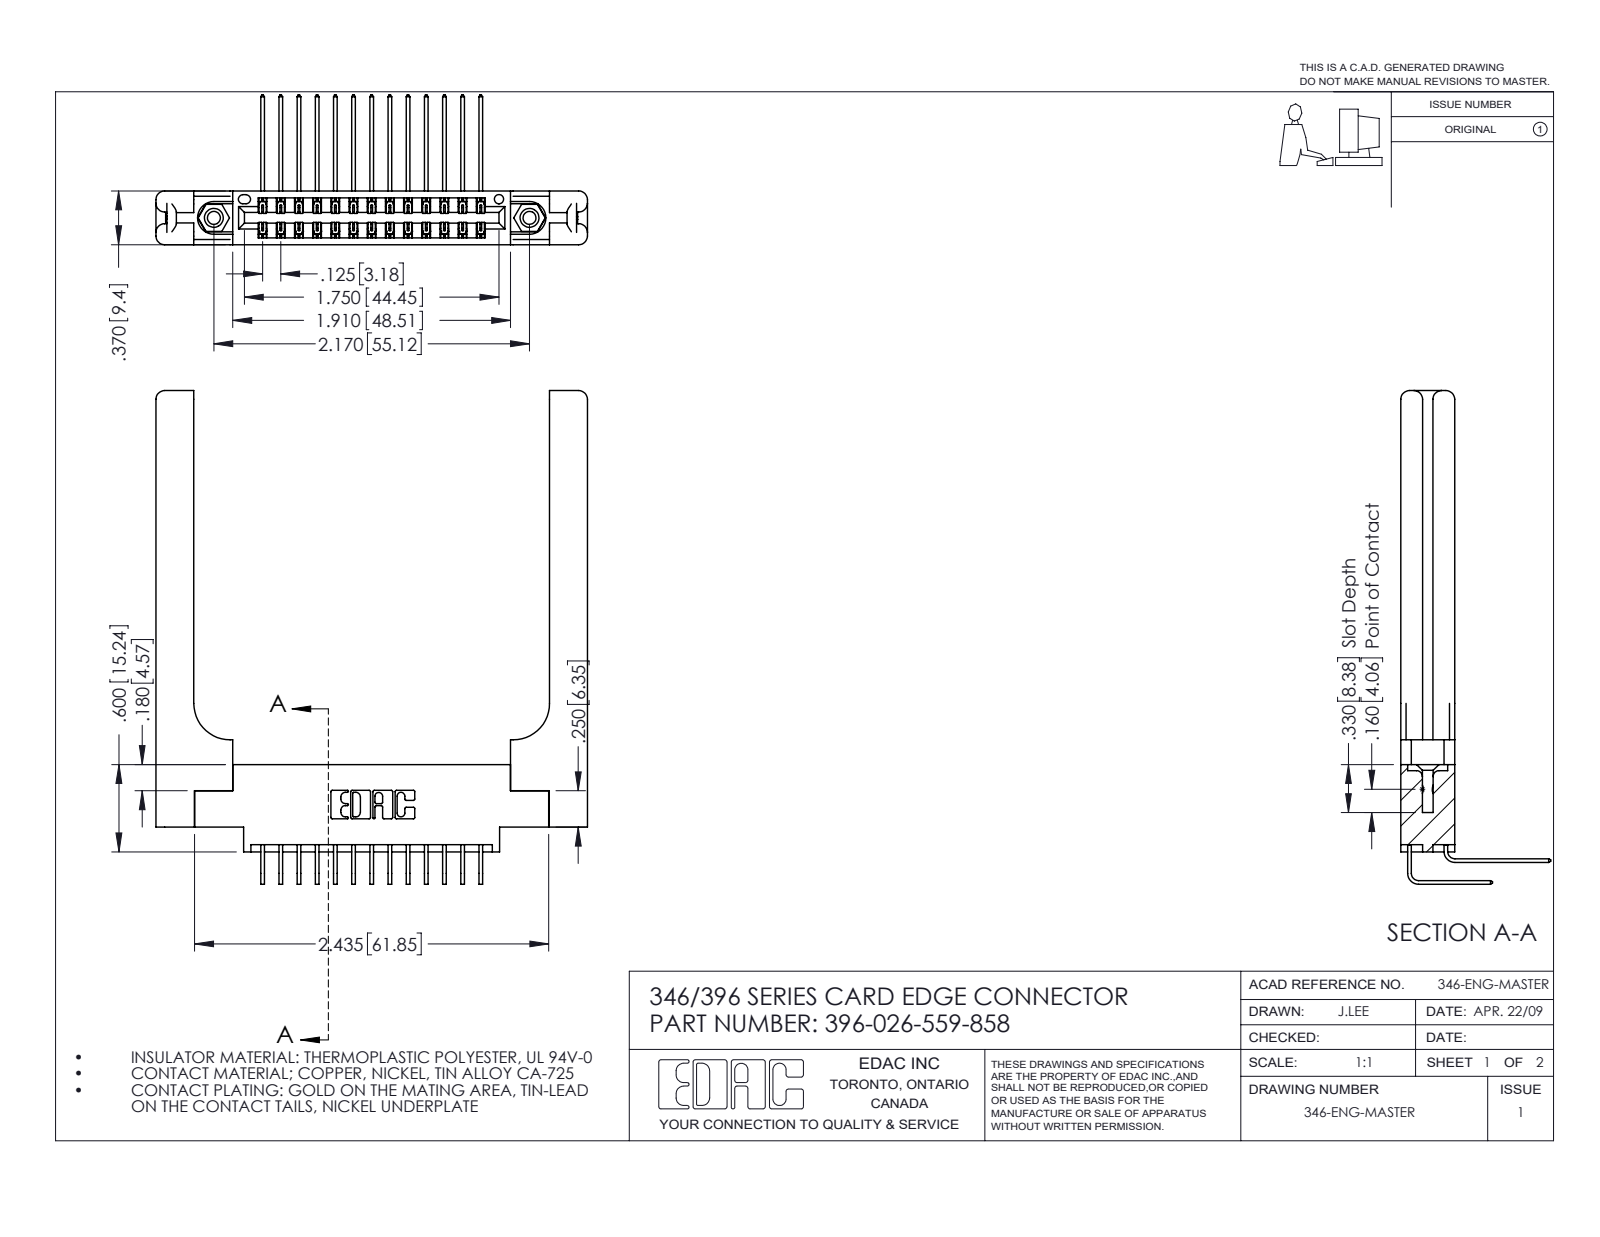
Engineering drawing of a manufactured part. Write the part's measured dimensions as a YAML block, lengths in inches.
part_name: "346-220-058_345-220-058; 345-292-001_559 Tail - 2; 345-292-001_558 559 Tail - 1; 345-250-001_345-250-001-102 (+2 more)"
step_written_by: "SolidWorks 2016 (CONFIG_CONTROL_DESIGN)"
units: inches
bodies: {solids: 31, faces: 1786, planar: 1190, cylindrical: 536, other: 60}
overall_size: [3.393, 2.966, 1.03]
volume: 0.892
surface_area: 23.56
round_holes:
  - {diameter: 0.089, count: 2}
  - {diameter: 0.125, count: 2}
  - {diameter: 0.156, count: 2}
  - {diameter: 0.064, count: 1}
round_bosses_or_shafts:
  - {diameter: 0.155, count: 2}
partial_cylinders:
  - {radius: 0.006, count: 39}
  - {radius: 0.01, count: 22}
  - {radius: 0.06, count: 16}
  - {radius: 0.007, count: 6}
  - {radius: 0.031, count: 6}
  - {radius: 0.026, count: 3}
  - {radius: 0.014, count: 2}
  - {radius: 0.022, count: 2}
face_to_face_distances: [0.37, 0.15, 0.072, 0.048, 0.148, 0.322, 0.025, 0.25, 0.22, 0.102]
hole_center_spacings: [0.246, 1.964, 2.17]
